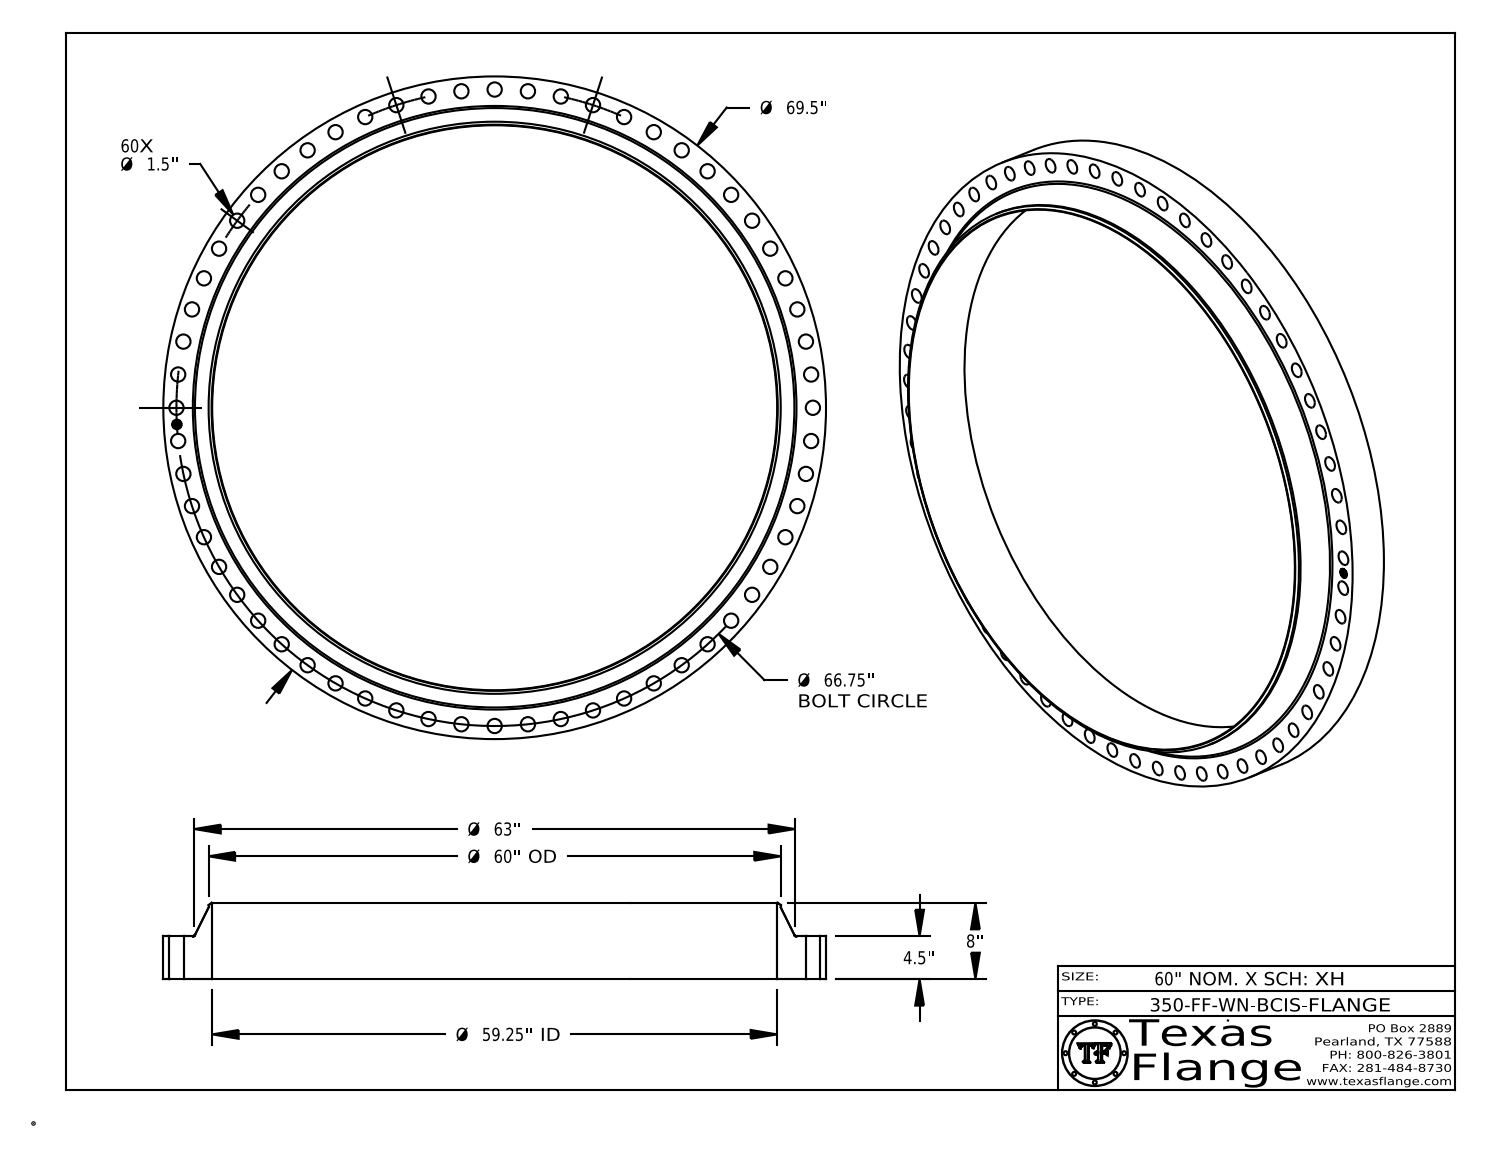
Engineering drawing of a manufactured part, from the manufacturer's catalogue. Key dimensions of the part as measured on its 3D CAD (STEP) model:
Part name (STEP PRODUCT): 350-FF-WN, BCIS
STEP written by: CATIA V5 STEP AP214 (AUTOMOTIVE_DESIGN)
Units: inches
Bodies: 1 solid, 520 faces (368 planar, 146 cylindrical, 6 other)
Overall size (bounding box): 69.5 × 69.5 × 8
Volume: 4 861 in³ · Surface area: 6 021 in²
Round holes (diameter × count): ⌀1.5 ×60, ⌀1 ×1, ⌀59.25 ×1
Round bosses / shafts (diameter × count): ⌀0.061 ×8, ⌀69.5 ×1, ⌀60 ×1, ⌀0.788 ×1
Main face-to-face distances: 4.5, 8, 3.5, 0.015, 4.485, 3.515, 0.298, 0.293, 0.019, 0.054
Hole centre spacings: 33.375, 3.493, 10.442, 66.384, 6.977, 66.658, 65.928, 13.878
